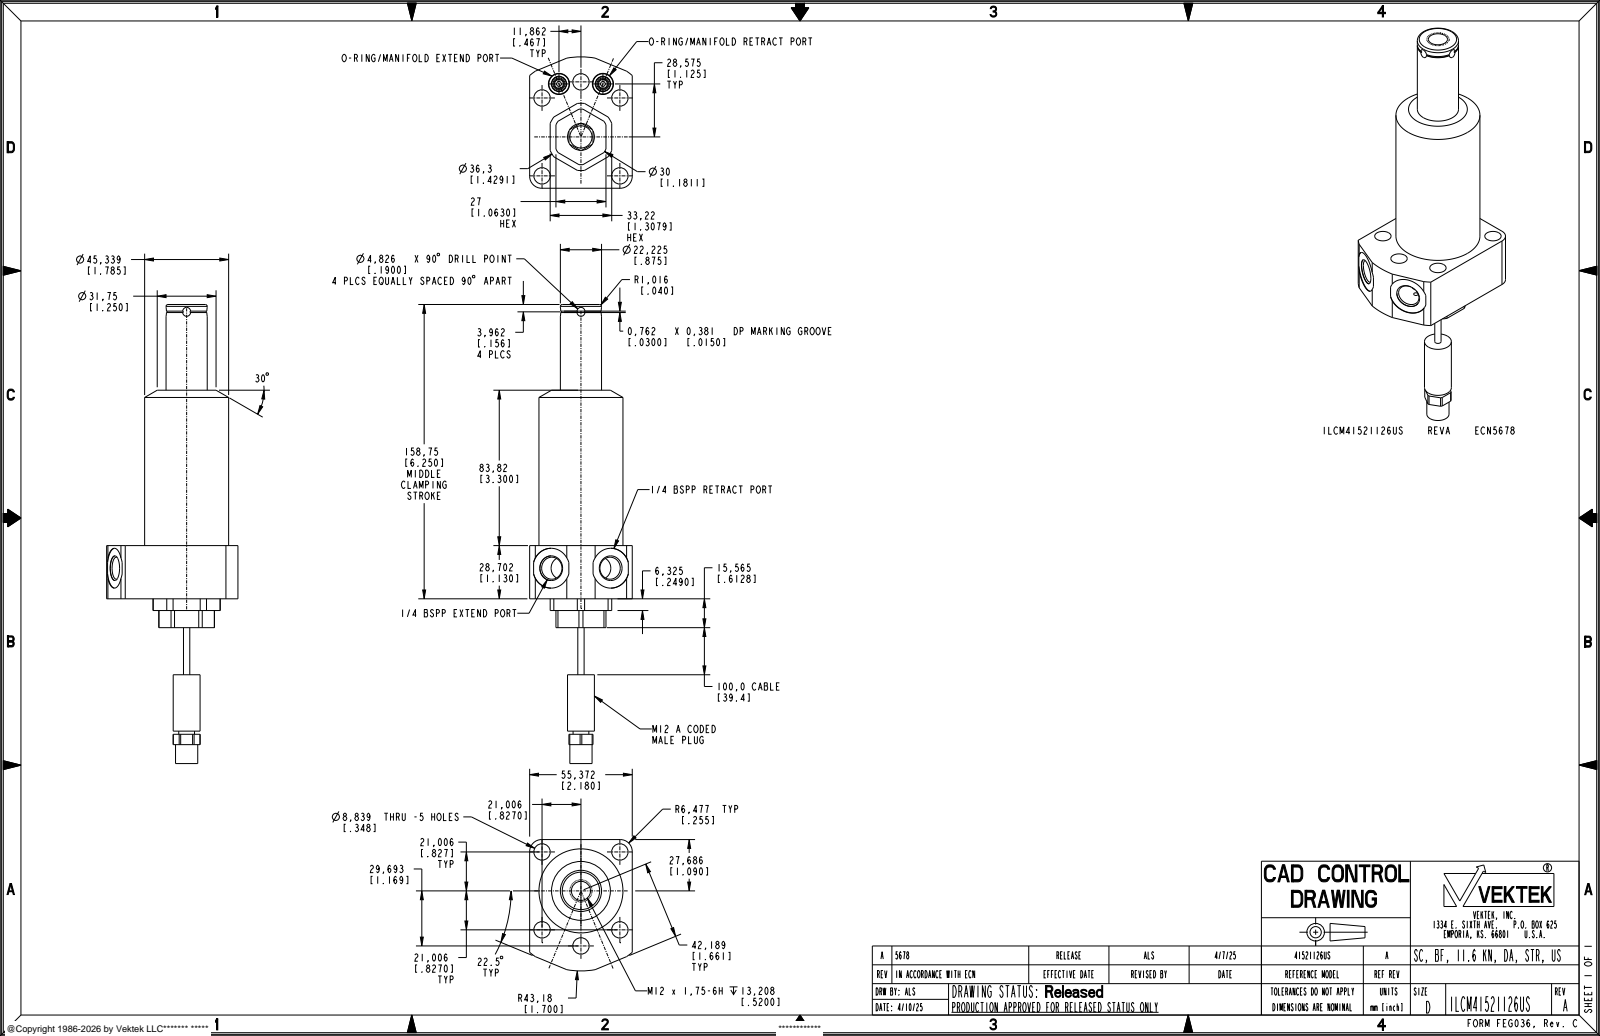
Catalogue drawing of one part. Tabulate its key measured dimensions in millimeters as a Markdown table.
| quantity | value |
| --- | --- |
| part name | ILCM41521126US |
| STEP written by | CREO PARAMETRIC BY PTC INC, 2021164 (AUTOMOTIVE_DESIGN) |
| units | millimeters |
| bodies | 1 solid, 188 faces (75 planar, 83 cylindrical, 30 other) |
| overall size | 247.62 × 86.87 × 63.37 |
| volume | 262 942 mm³ |
| surface area | 39 448 mm² |
| round holes (diameter × count) | 8.84 × 5, 2.49 × 2, 6.5 × 2, 11.4 × 2, 11.89 × 2, 13.31 × 2, 21.5 × 2, 10.31 × 1 |
| round bosses / shafts (diameter × count) | 5.49 × 2, 45.34 × 1, 22.23 × 1, 14.5 × 1, 11.99 × 1, 11.99 × 1, 8.51 × 1, 3.4 × 1 |
| partial cylindrical surfaces (radius × count) | 6.48 × 2, 10.73 × 1, 15 × 1, 18.15 × 1, 43.18 × 1 |
| main face-to-face distances | 28.7, 55.38, 15.57, 44.27, 3.11, 30.11, 128.09, 112.52, 83.82, 27 |
| hole center spacings | 29.71, 42.02, 11.87, 11.91, 22.73, 30.93, 33.73, 50.42 |
